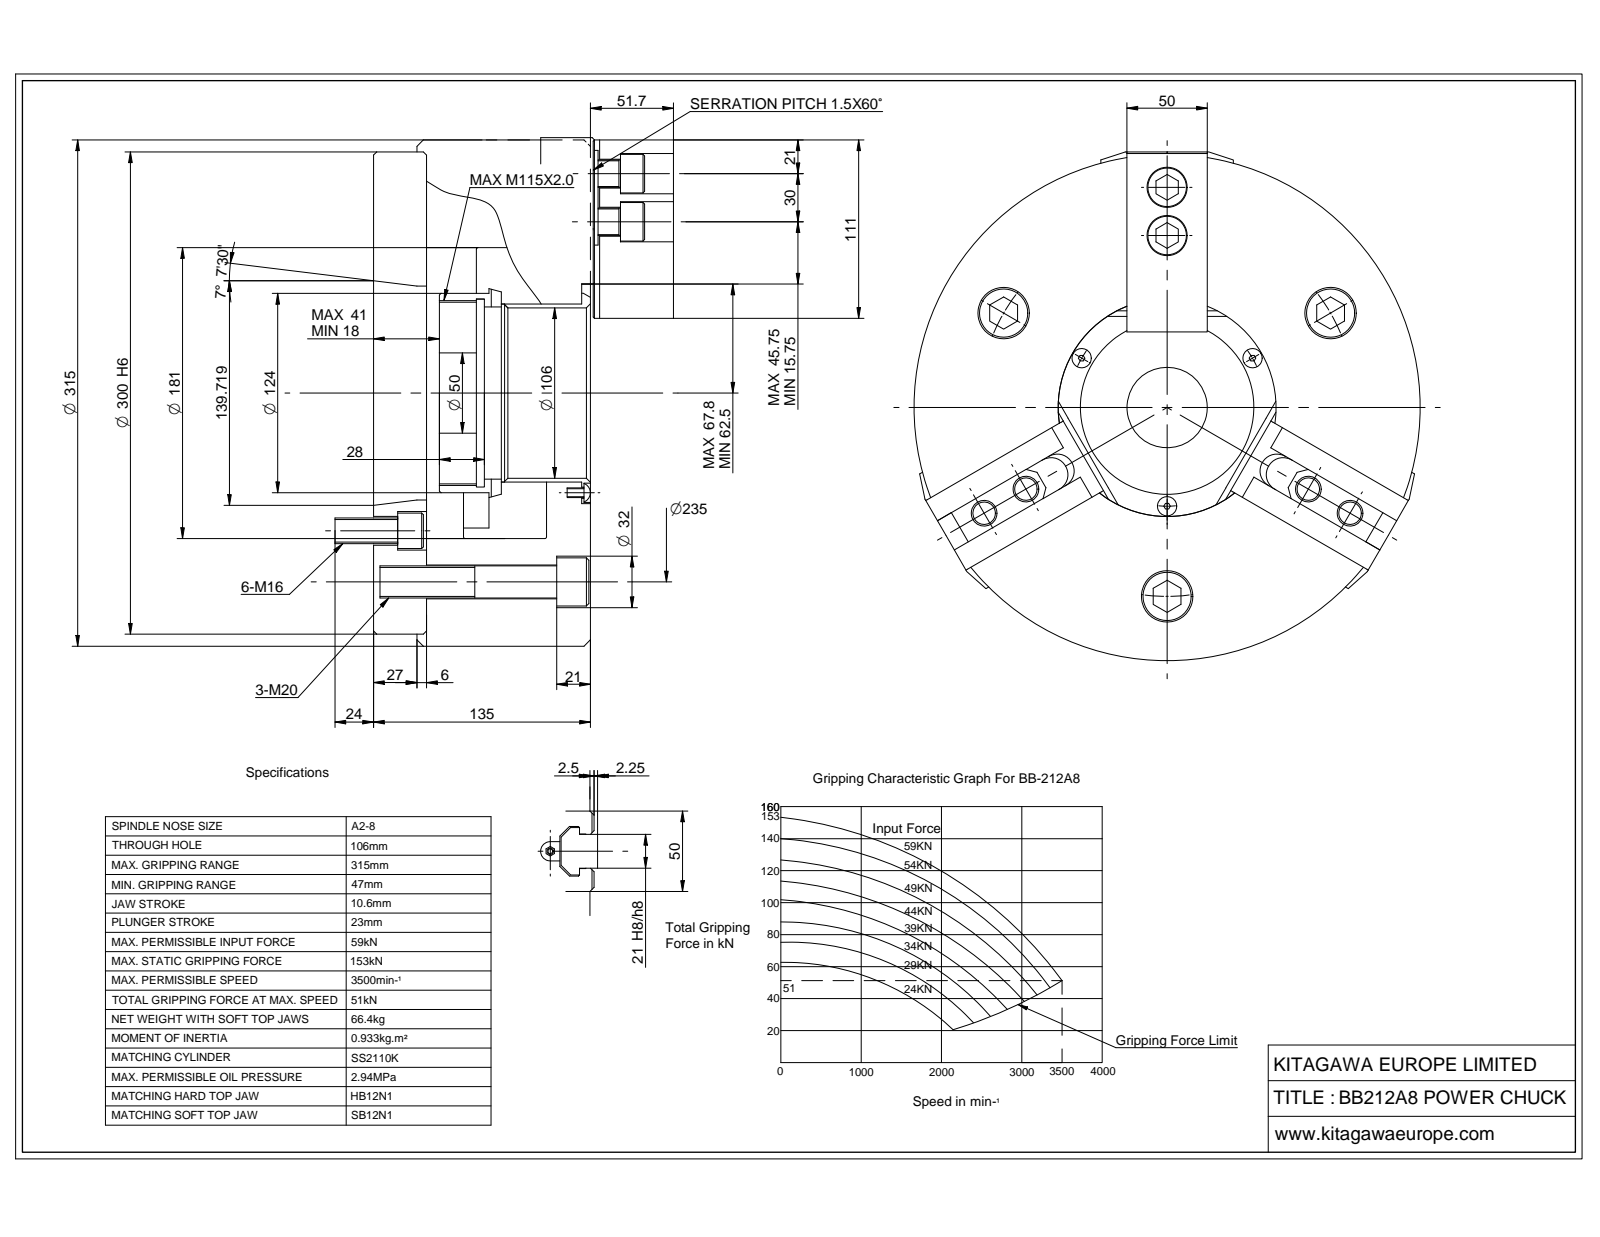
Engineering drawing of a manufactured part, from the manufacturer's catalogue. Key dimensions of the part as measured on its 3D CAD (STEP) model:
Part name (STEP PRODUCT): BB212A8
STEP written by: ST-DEVELOPER v16.7 (AUTOMOTIVE_DESIGN)
Units: millimetres
Bodies: 1 solid, 4418 faces (3648 planar, 342 cylindrical, 428 other)
Overall size (bounding box): 315.74 × 315 × 210.73
Volume: 9 130 000 mm³ · Surface area: 764 626 mm²
Round holes (diameter × count): ⌀17 ×18, ⌀3.8 ×12, ⌀25 ×12, ⌀10 ×9, ⌀11 ×9, ⌀6 ×7, ⌀8.5 ×6, ⌀14 ×6, ⌀16 ×6, ⌀17.29 ×6, ⌀4.92 ×4, ⌀2 ×3
Round bosses / shafts (diameter × count): ⌀24 ×12, ⌀16 ×12, ⌀30 ×3, ⌀20 ×3, ⌀10.5 ×3, ⌀315 ×1, ⌀181 ×1
Partial cylindrical surfaces — rounded edges, fillets, slot ends (radius × count): R7 ×17, R0.4 ×12, R0.49 ×12, R0.6 ×12, R0.8 ×6, R1.4 ×6, R2 ×6, R6.5 ×6
Main face-to-face distances: 134, 1, 50, 135, 41.5, 60, 40.5, 70.5, 33, 32
Hole centre spacings: 30.4, 60.75, 71.5, 75.93, 98.29, 104.17, 105.47, 117.5
